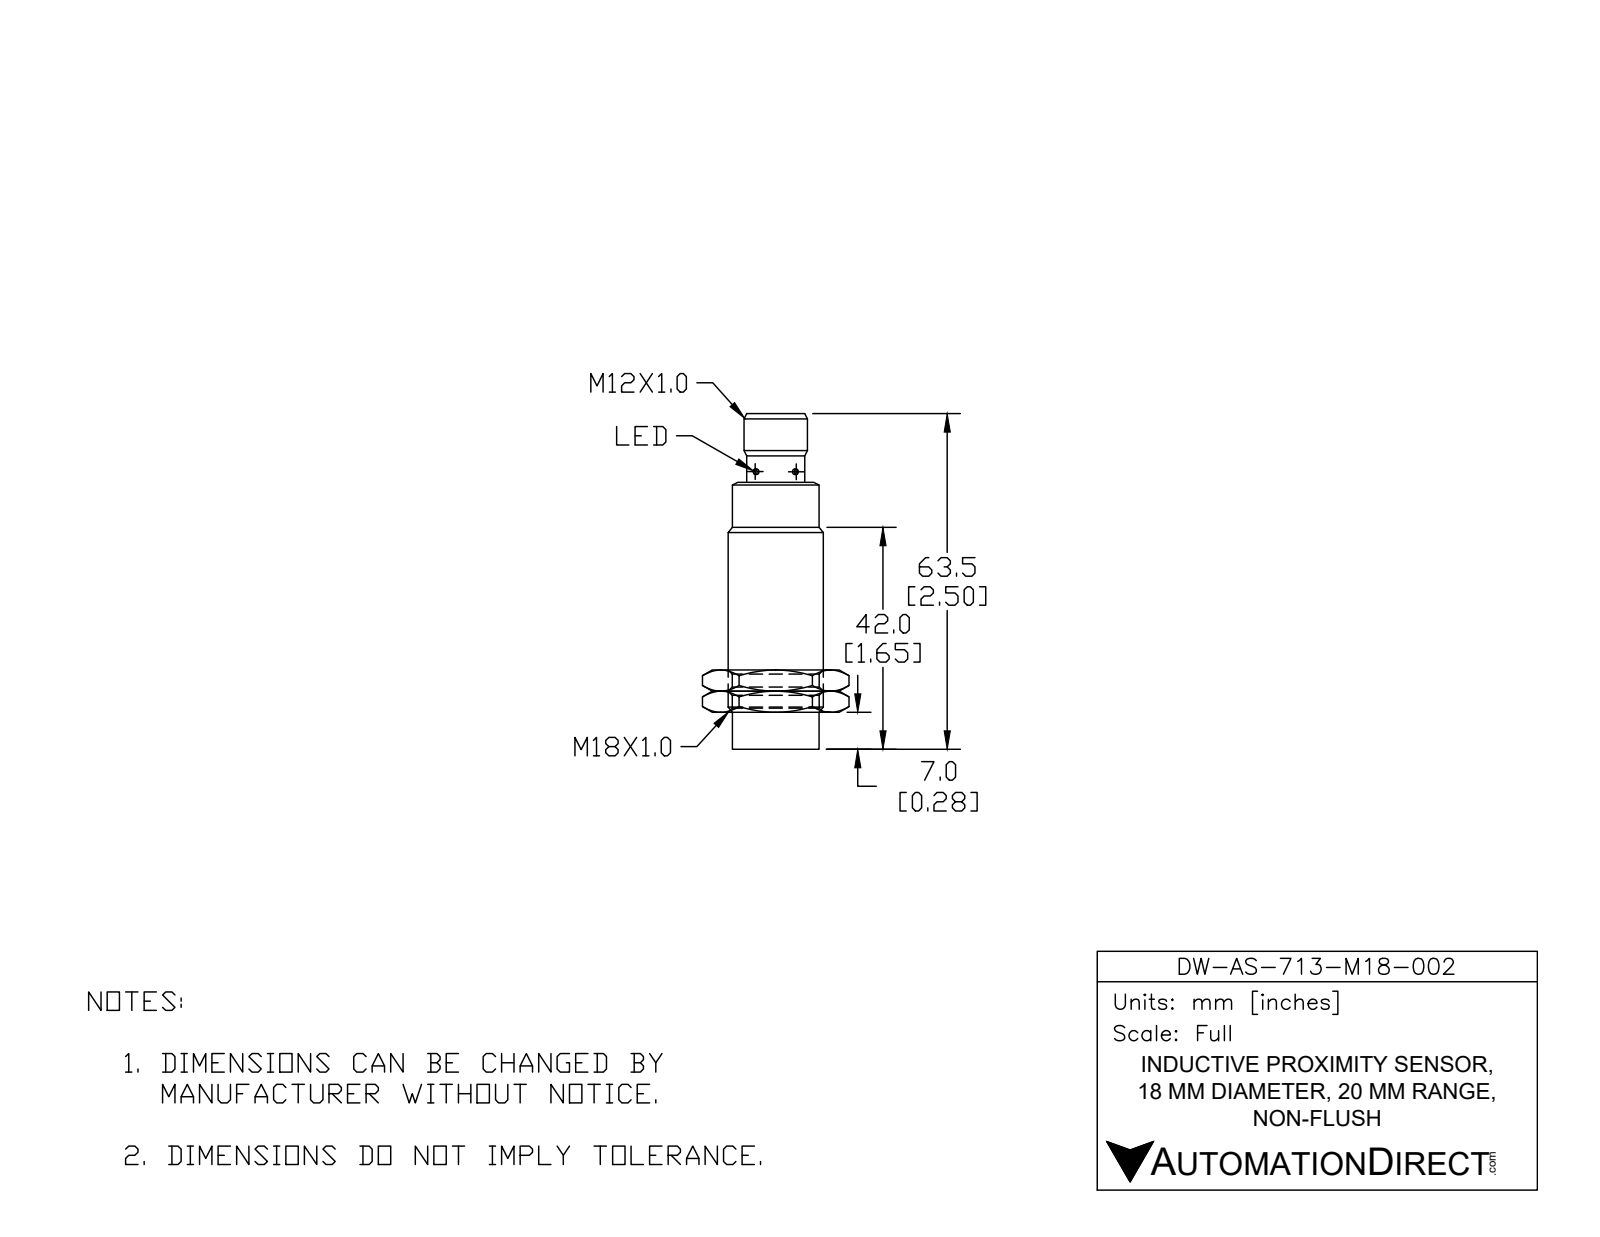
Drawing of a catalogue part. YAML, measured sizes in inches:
part_name: "DW-AS-713-M18-002"
step_written_by: "SolidWorks 2017 (AUTOMOTIVE_DESIGN)"
units: inches
bodies: {solids: 1, faces: 40, planar: 8, cylindrical: 17, other: 15}
overall_size: [2.5, 0.709, 0.709]
volume: 0.778
surface_area: 6.608
round_holes:
  - {diameter: 0.118, count: 2}
  - {diameter: 0.335, count: 1}
round_bosses_or_shafts:
  - {diameter: 0.04, count: 4}
  - {diameter: 0.709, count: 1}
  - {diameter: 0.646, count: 1}
  - {diameter: 0.459, count: 1}
  - {diameter: 0.415, count: 1}
partial_cylinders:
  - {radius: 0.02, count: 2}
face_to_face_distances: [2.157, 1.988, 0.169, 2.5, 0.512, 0.343, 0.276, 1.713, 1.882, 2.224]
